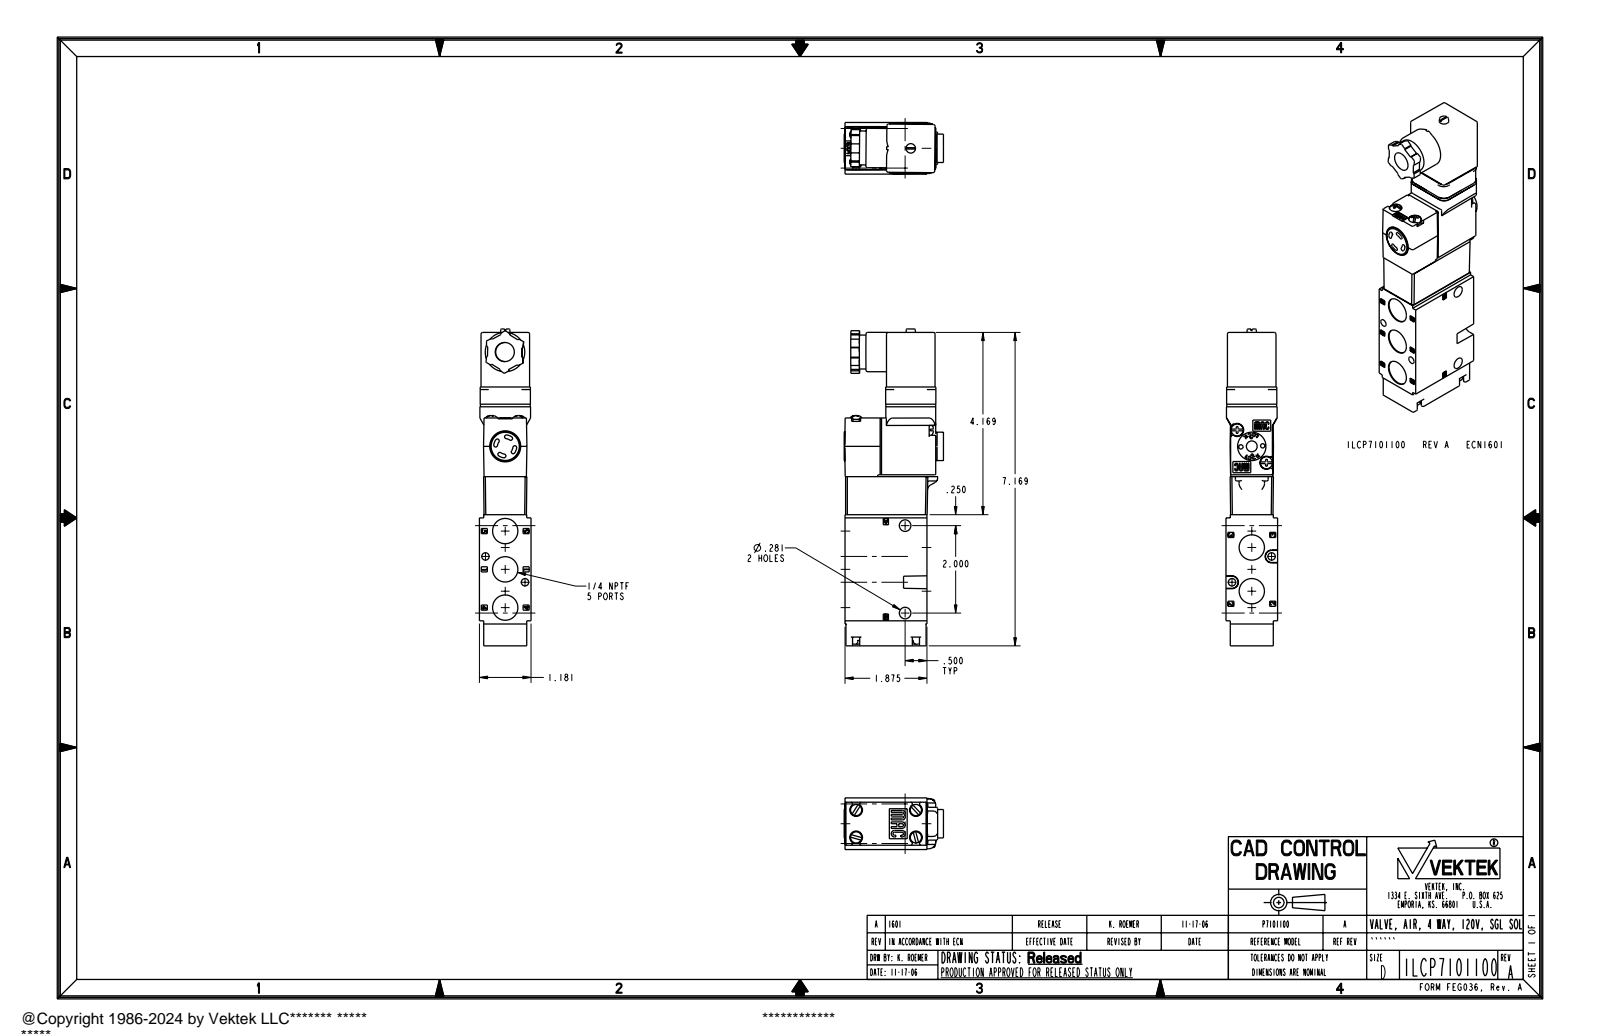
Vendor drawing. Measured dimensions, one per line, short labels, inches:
name: ILCP7101100
written by: PRO/ENGINEER BY PARAMETRIC TECHNOLOGY CORPORATION, 2005180 (AUTOMOTIVE_DESIGN_CC2)
unit: in
bodies: 2 solids, 1292 faces (759 planar, 278 cylindrical, 255 other)
size: 7.248 × 2.272 × 1.181
volume: 12.91 in³; area: 65 in²
holes: 5× ⌀0.579, 4× ⌀0.138, 2× ⌀0.098, 2× ⌀0.11, 2× ⌀0.126, 2× ⌀0.169, 2× ⌀0.254, 2× ⌀0.265, 2× ⌀0.287, 1× ⌀0.108, 1× ⌀0.11, 1× ⌀0.236
bosses: 4× ⌀0.276, 4× ⌀0.256, 2× ⌀0.65, 2× ⌀0.267, 1× ⌀0.901, 1× ⌀0.776, 1× ⌀0.686, 1× ⌀0.311
rounds: 24× R0.008, 20× R0.039, 14× R0.01, 13× R0.02, 13× R0.031, 12× R0.157, 8× R0.035, 8× R0.043
face distances: 1.181, 0.02, 0.098, 1.083, 1.875, 1.856, 1.102, 1.122, 1.598, 0.071
hole spacings: 0.515, 1.023, 1.03, 0.5, 0.25, 0.375, 0.497, 0.508
